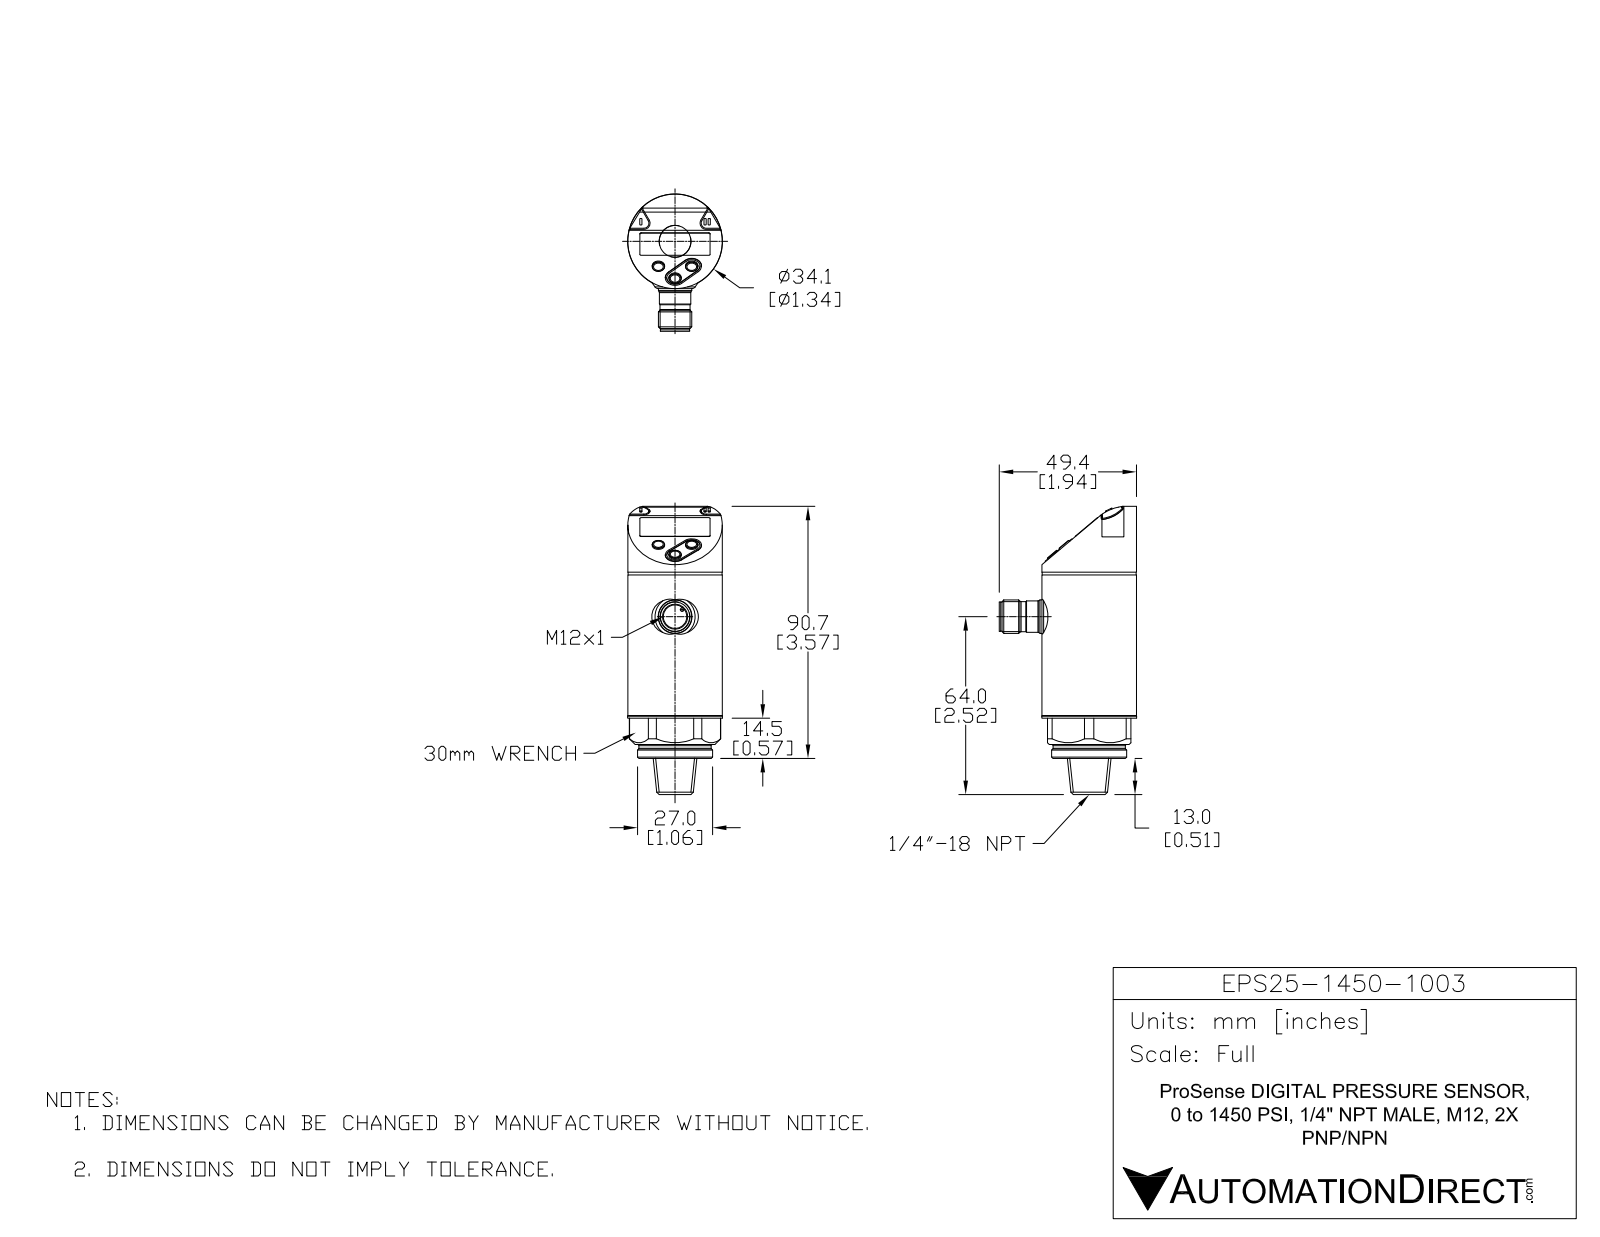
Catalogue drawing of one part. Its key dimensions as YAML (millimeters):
part_name: "EPS25-V1450-1003"
step_written_by: "SolidWorks 2016 (AUTOMOTIVE_DESIGN)"
units: millimeters
bodies: {solids: 11, faces: 370, planar: 207, cylindrical: 84, other: 79}
overall_size: [103.7, 49.4, 34.1]
volume: 72203
surface_area: 21365
round_holes:
  - {diameter: 4.2, count: 1}
  - {diameter: 8.45, count: 1}
round_bosses_or_shafts:
  - {diameter: 1.4, count: 4}
  - {diameter: 1, count: 4}
  - {diameter: 34.1, count: 1}
  - {diameter: 34, count: 1}
  - {diameter: 33.8, count: 1}
  - {diameter: 27, count: 1}
  - {diameter: 26, count: 1}
  - {diameter: 12, count: 1}
partial_cylinders:
  - {radius: 1.8, count: 2}
  - {radius: 2.2, count: 2}
  - {radius: 3, count: 2}
  - {radius: 3.5, count: 2}
  - {radius: 15, count: 2}
  - {radius: 0.61, count: 1}
  - {radius: 6.8, count: 1}
  - {radius: 16.44, count: 1}
face_to_face_distances: [0.68, 11.5, 12.18, 10.68, 1.5, 10, 2, 2.5, 14, 4]
